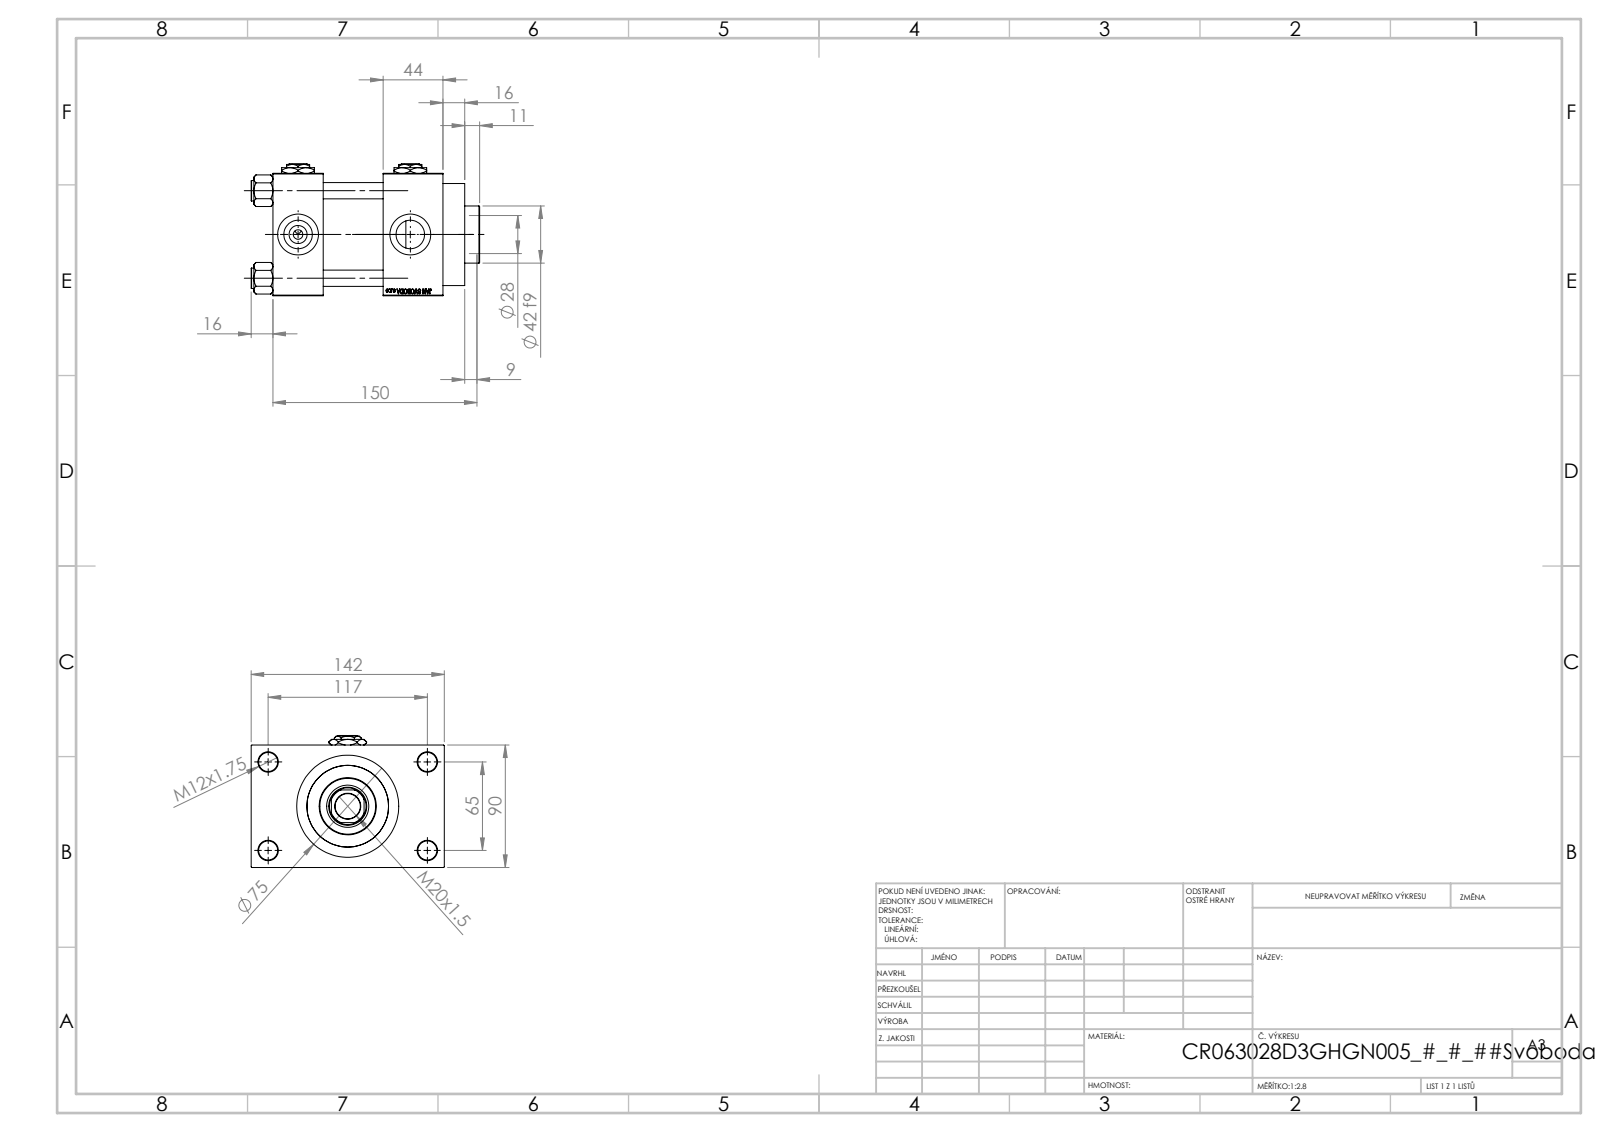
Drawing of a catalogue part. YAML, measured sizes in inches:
part_name: "V215CR_D_TYCINKA; V215CR_VCP_D; Zatka_pro_OIL_PORT; V215CR_D_Body (+2 more)"
step_written_by: "SolidWorks 2019 (CONFIG_CONTROL_DESIGN)"
units: inches
bodies: {solids: 13, faces: 1204, planar: 545, cylindrical: 99, other: 560}
overall_size: [6.614, 5.591, 3.819]
volume: 62.37
surface_area: 297.4
round_holes:
  - {diameter: 0.472, count: 4}
  - {diameter: 0.551, count: 4}
  - {diameter: 0.825, count: 4}
  - {diameter: 1.181, count: 4}
  - {diameter: 0.276, count: 3}
  - {diameter: 0.728, count: 1}
  - {diameter: 1.102, count: 1}
  - {diameter: 1.22, count: 1}
  - {diameter: 1.969, count: 1}
  - {diameter: 2.362, count: 1}
  - {diameter: 2.48, count: 1}
round_bosses_or_shafts:
  - {diameter: 0.591, count: 4}
  - {diameter: 2.953, count: 1}
  - {diameter: 2.717, count: 1}
  - {diameter: 1.654, count: 1}
partial_cylinders:
  - {radius: 0.531, count: 1}
face_to_face_distances: [1.732, 3.543, 3.189, 1.457, 3.465, 4.921, 1.024, 4.567, 0.63, 5.551]
hole_center_spacings: [1.037, 1.79, 2.531, 2.635, 2.748, 3.569, 4.383, 2.559]
